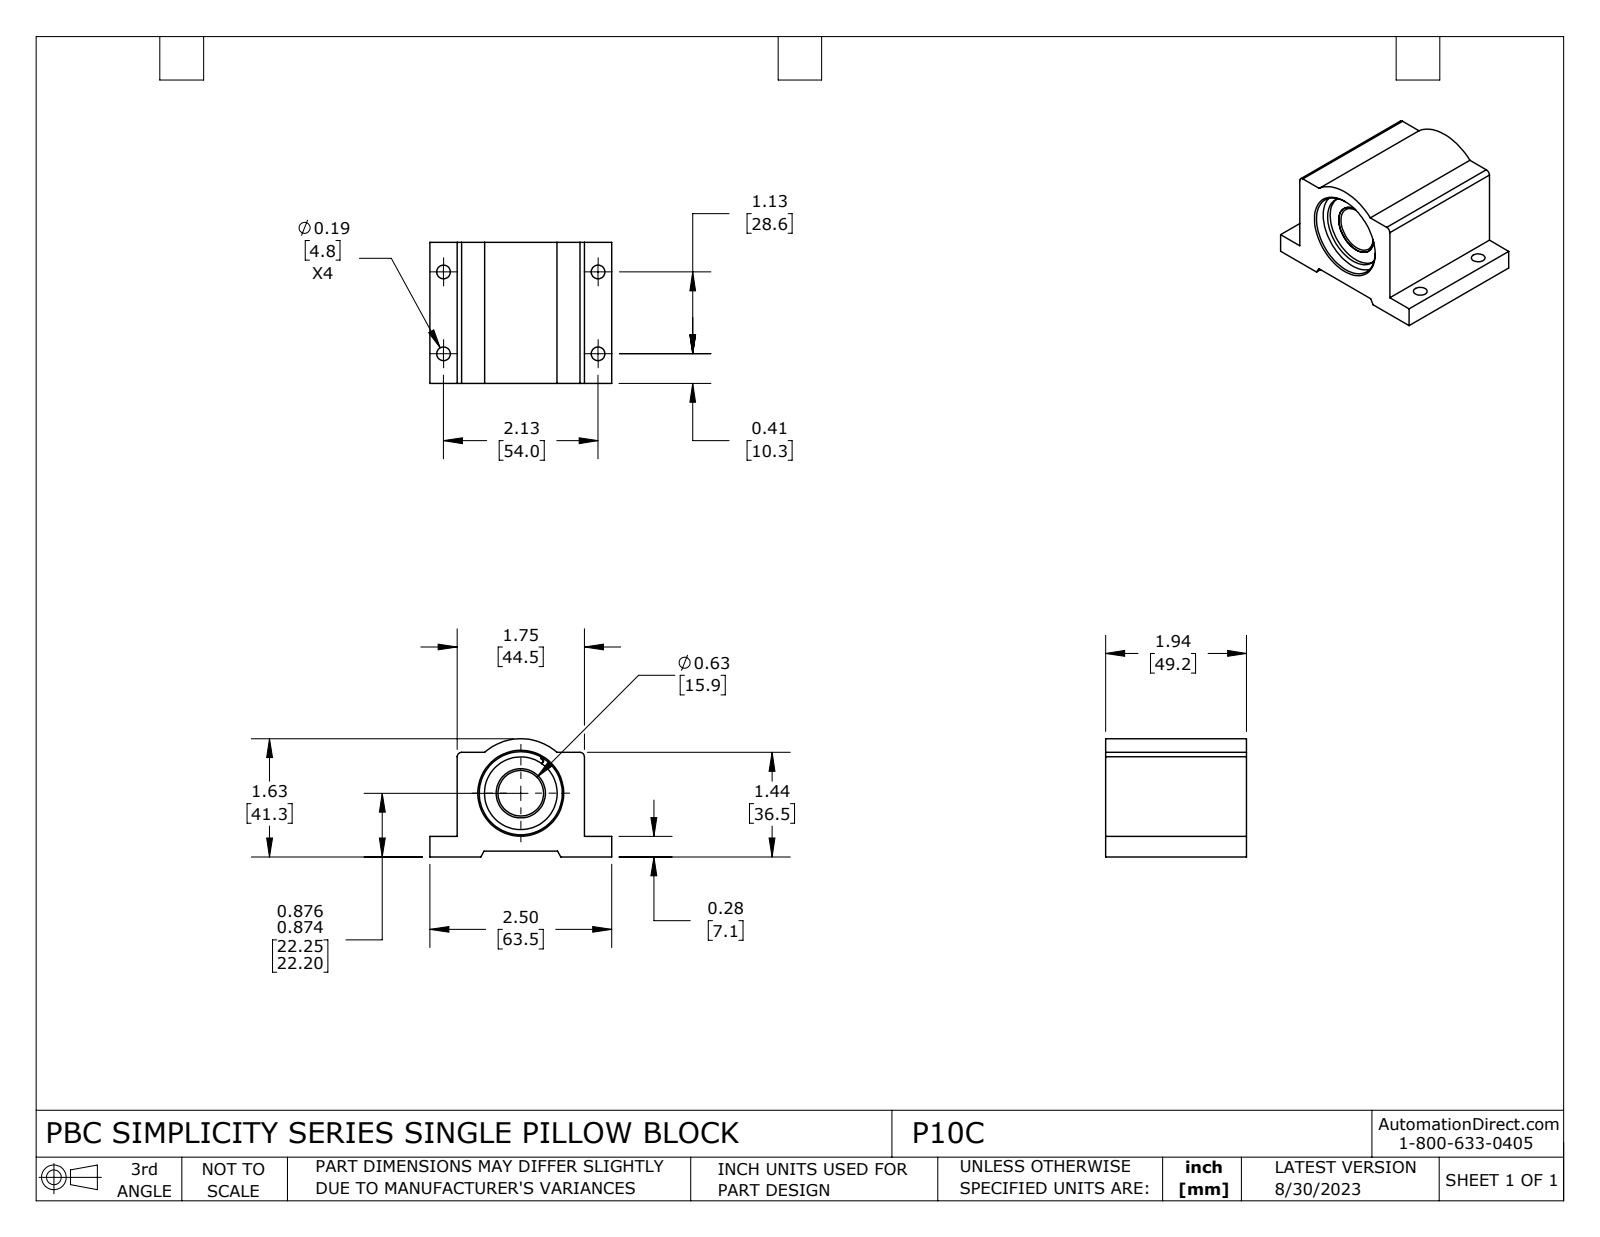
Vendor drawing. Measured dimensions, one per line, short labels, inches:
name: P10C
written by: SolidWorks 2021 (CONFIG_CONTROL_DESIGN)
unit: in
bodies: 7 solids, 164 faces (45 planar, 71 cylindrical, 48 other)
size: 2.5 × 1.937 × 1.625
volume: 4.378 in³; area: 48.03 in²
holes: 4× ⌀0.187, 1× ⌀0.626, 1× ⌀0.677, 1× ⌀0.999, 1× ⌀1.141, 1× ⌀1.197
bosses: 1× ⌀1.205, 1× ⌀1.124, 1× ⌀1.06, 1× ⌀0.962
rounds: 4× R0.017, 2× R0.012, 2× R0.022, 2× R0.06, 1× R0.75
face distances: 1.75, 0.08, 1.938, 0.281, 0.201, 1.437, 1.357, 1.156, 0.375, 2.125
hole spacings: 1.125, 2.125, 2.405
